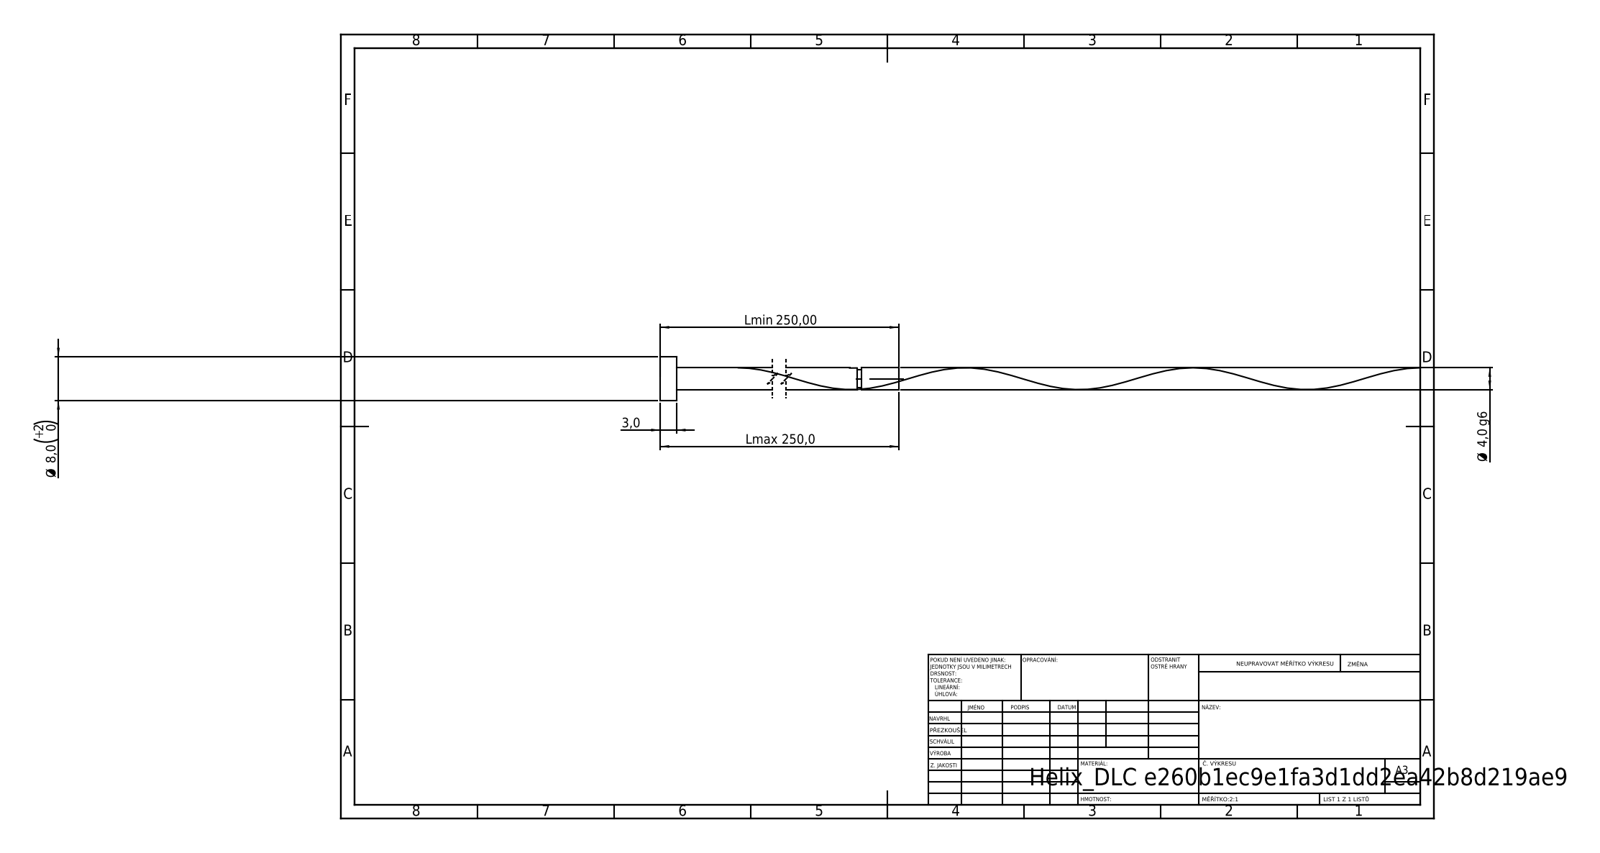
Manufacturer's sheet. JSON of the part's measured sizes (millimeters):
{"step_written_by": "SolidWorks 2019 (CONFIG_CONTROL_DESIGN)", "units": "millimeters", "bodies": {"solids": 1, "faces": 16, "planar": 6, "cylindrical": 9, "other": 1}, "overall_size": [250, 8, 8], "volume_mm3": 3920, "surface_area_mm2": 4385, "round_bosses_or_shafts": [[8, 1], [4, 1], [3.2, 1]], "face_to_face_distances": [3, 250, 247, 243.16, 240.16, 6.84, 242.36, 239.36, 0.8, 7.64]}
